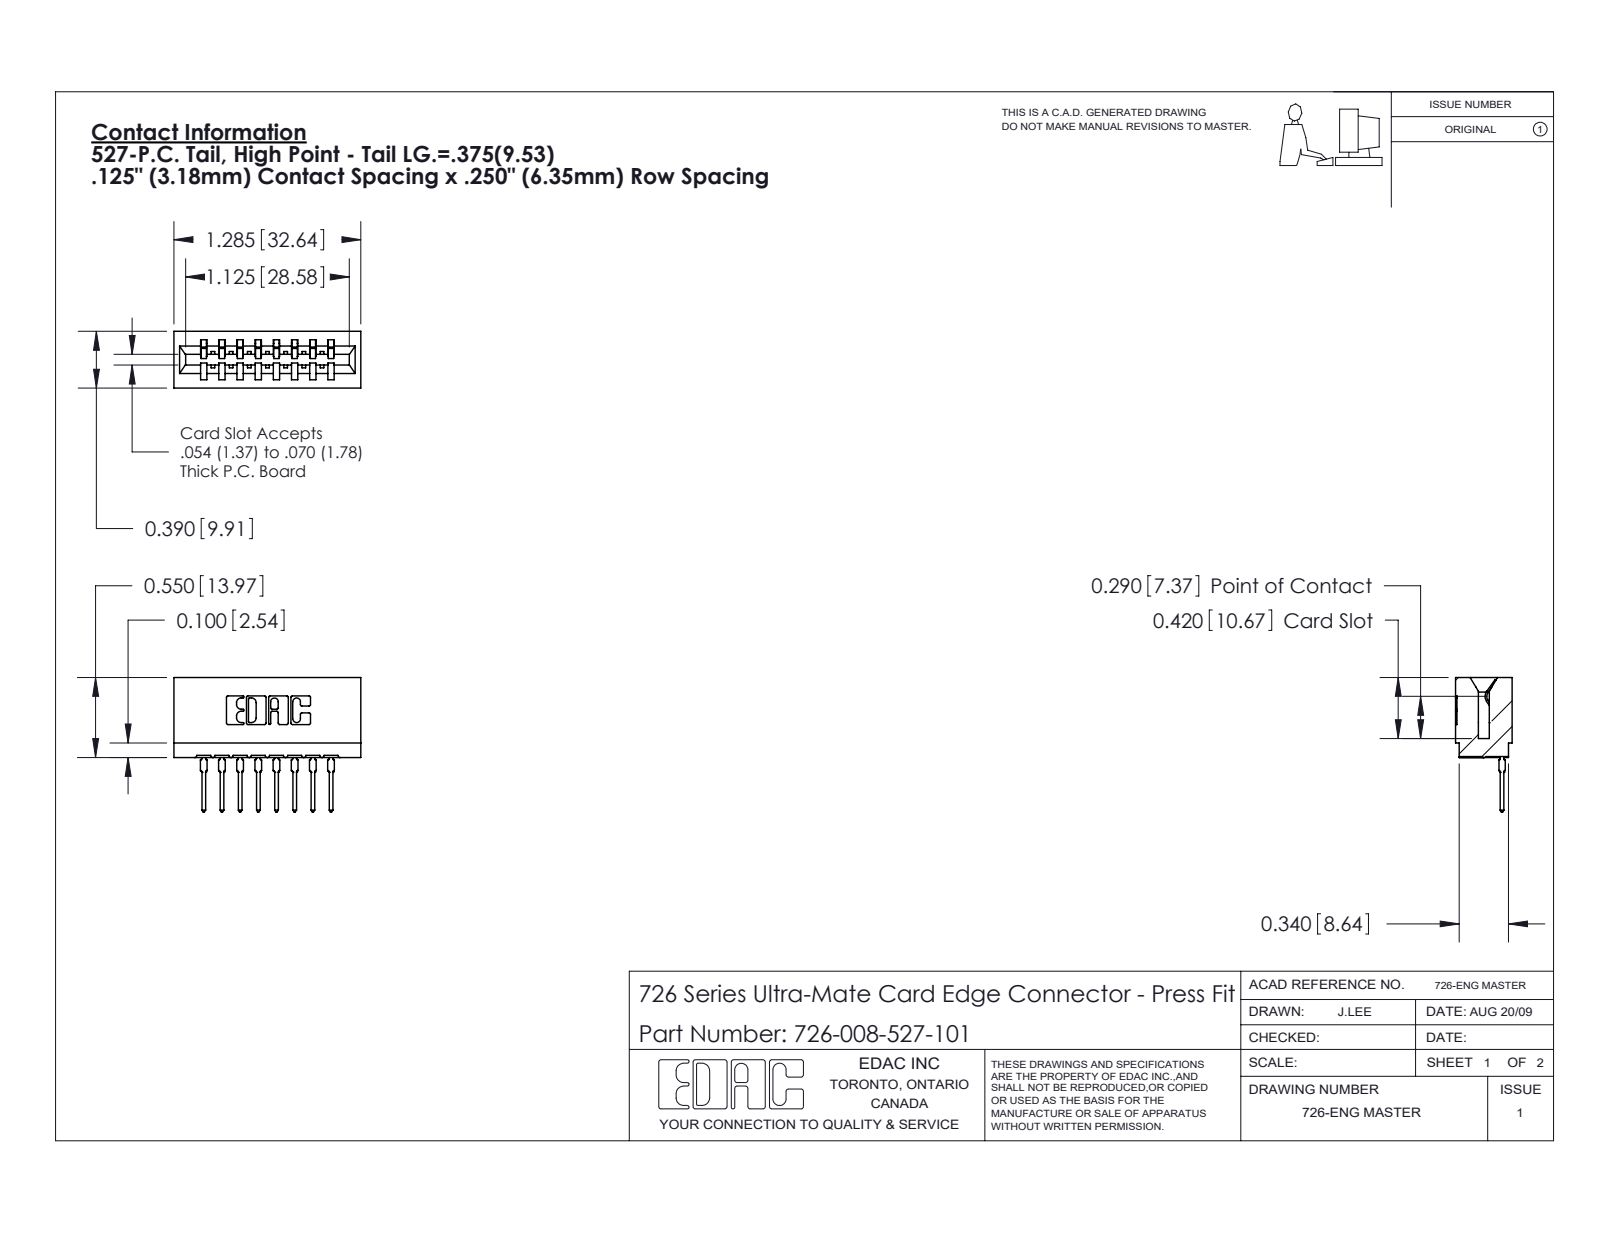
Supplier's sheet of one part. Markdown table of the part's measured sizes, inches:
| quantity | value |
| --- | --- |
| part name | 726-008-527-101; 746-292-001_527; 726 Part_.515 Slot Depth - 01 |
| STEP written by | SolidWorks 2020 (CONFIG_CONTROL_DESIGN) |
| units | inches |
| bodies | 9 solids, 961 faces (559 planar, 194 cylindrical, 208 other) |
| overall size | 1.285 × 0.924 × 0.39 |
| volume | 0.19 in³ |
| surface area | 6.668 in² |
| partial cylindrical surfaces (radius × count) | 0.01 × 22, 0.021 × 16, 0.015 × 9, 0.007 × 6, 0.031 × 6, 0.005 × 4, 0.011 × 4, 0.026 × 3 |
| main face-to-face distances | 0.25, 0.042, 0.125, 0.5, 0.333, 0.057, 0.208, 0.125, 0.292, 0.375 |
